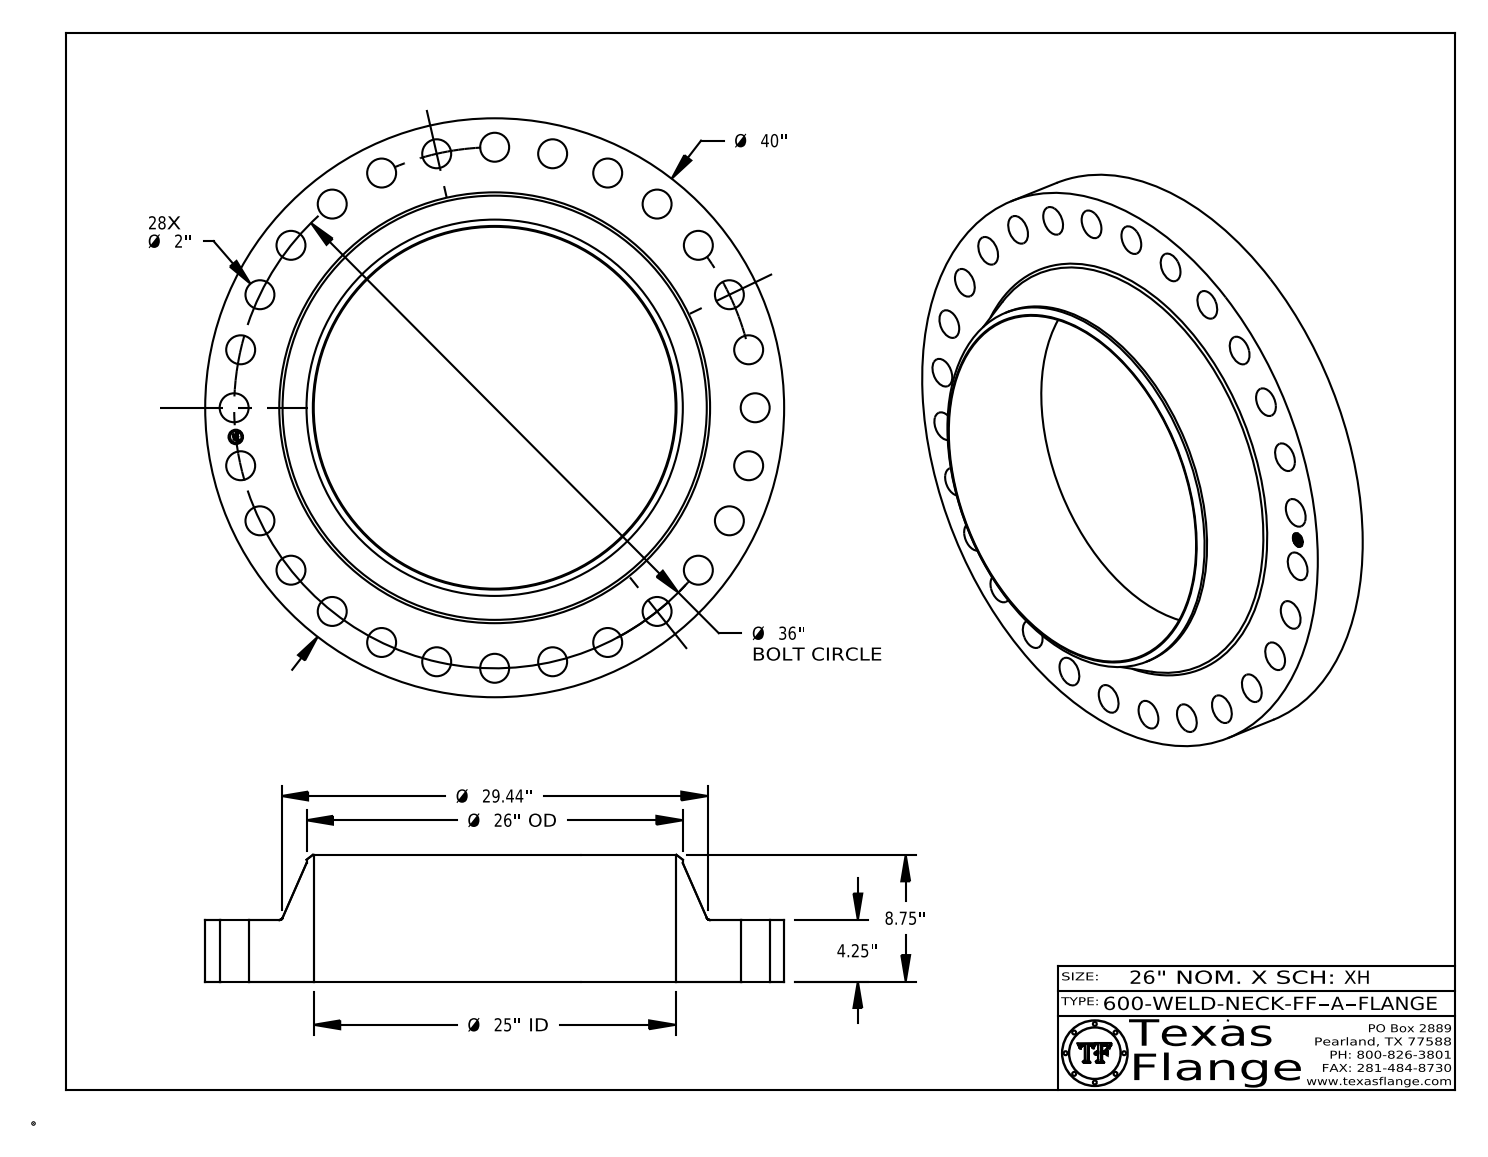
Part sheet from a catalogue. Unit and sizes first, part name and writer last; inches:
Units: inches
Overall size (bounding box): 40 × 40 × 8.75
Round holes (diameter × count): ⌀2 ×28, ⌀1 ×1, ⌀25 ×1
Round bosses / shafts (diameter × count): ⌀0.061 ×8, ⌀40 ×1, ⌀26 ×1, ⌀0.788 ×1
Main face-to-face distances: 4.25, 8.75, 4.5, 0.015, 4.235, 4.515, 0.298, 0.293, 0.054, 0.193
Hole centre spacings: 18, 19.153, 4.031, 8.011, 11.89, 15.62, 22.446, 25.456
Volume: 3 343 in³ · Surface area: 3 573 in²
Bodies: 1 solid, 456 faces (368 planar, 82 cylindrical, 6 other)
Part name (STEP PRODUCT): 600-WELD-NECK-FF, Series A
STEP written by: CATIA V5 STEP AP214 (AUTOMOTIVE_DESIGN)
